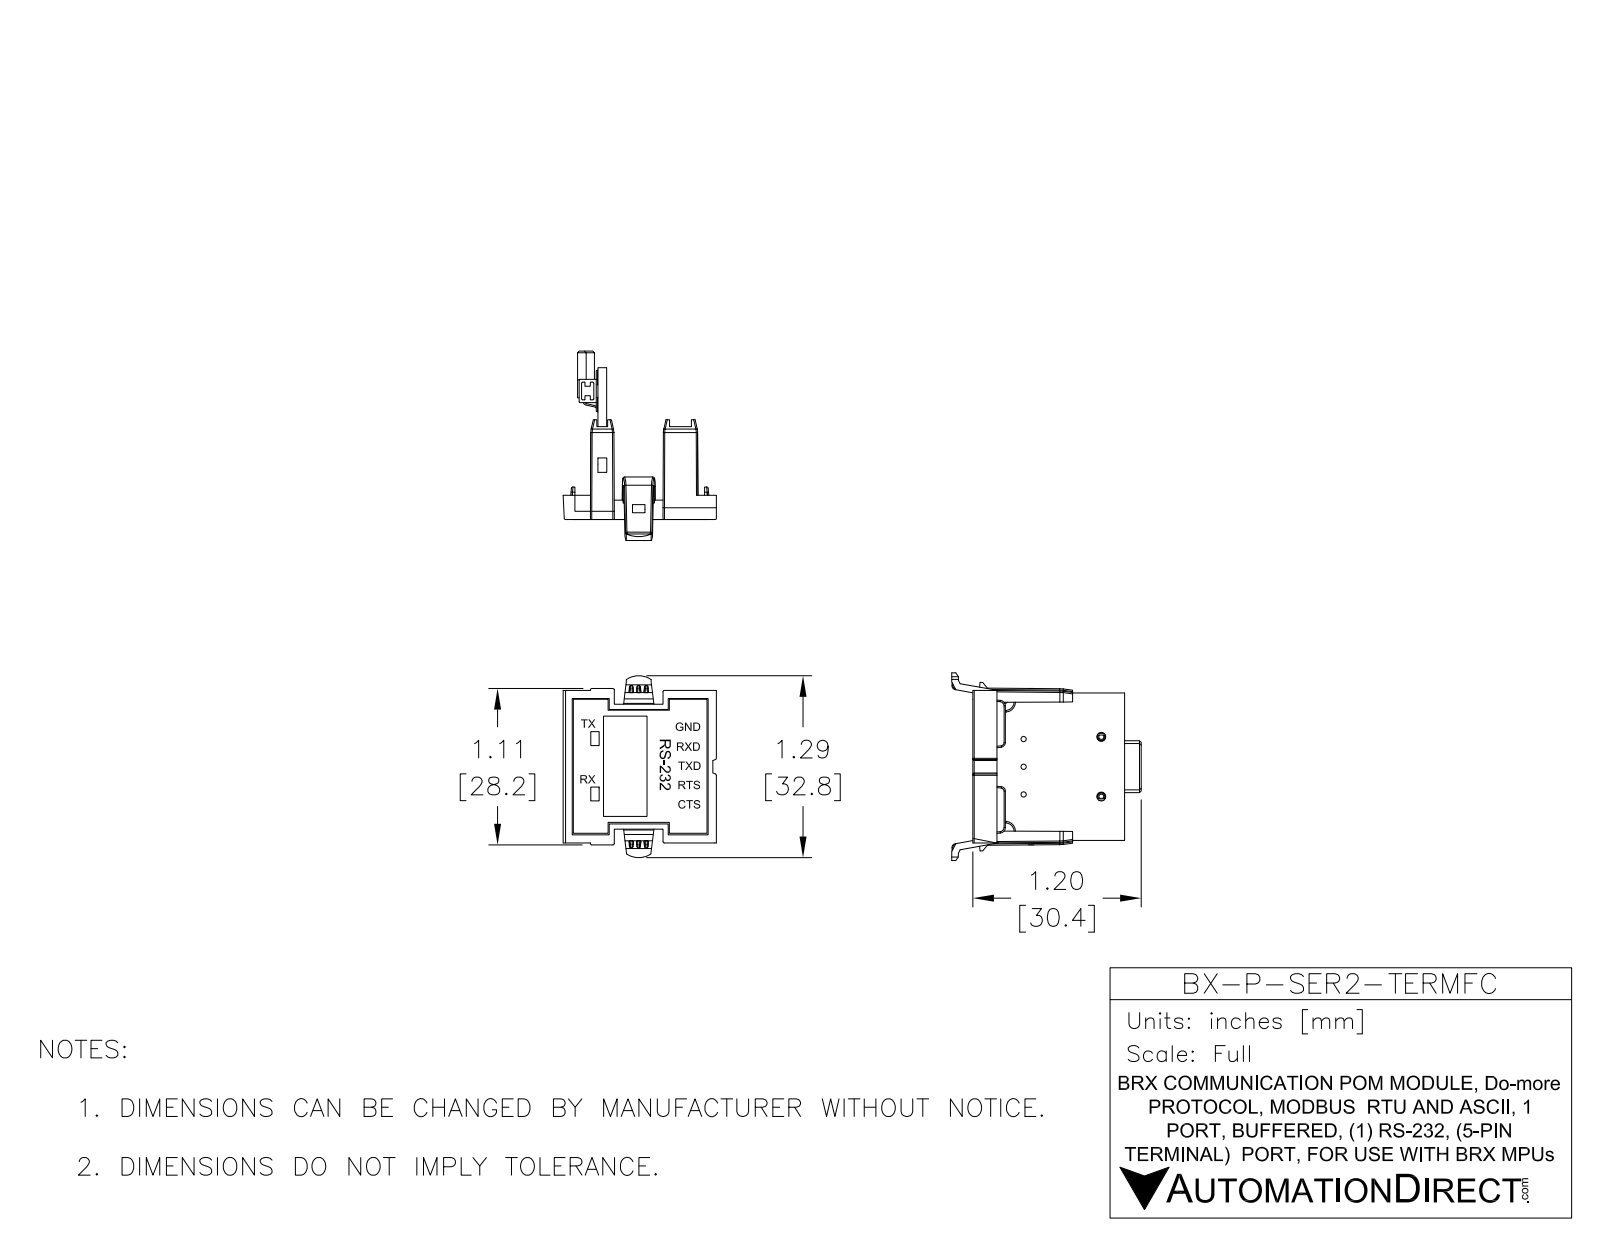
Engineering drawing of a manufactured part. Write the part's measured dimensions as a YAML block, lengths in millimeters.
part_name: "BX-P-SER2-TERMFC c r3"
step_written_by: "SolidWorks 2017 (AUTOMOTIVE_DESIGN)"
units: millimeters
bodies: {solids: 37, faces: 2056, planar: 1492, cylindrical: 367, other: 197}
overall_size: [41, 33.9, 27.5]
volume: 6190
surface_area: 10500
round_holes:
  - {diameter: 0.3, count: 5}
  - {diameter: 1, count: 5}
  - {diameter: 2, count: 5}
  - {diameter: 2.8, count: 5}
  - {diameter: 0.9, count: 3}
  - {diameter: 1.6, count: 2}
round_bosses_or_shafts:
  - {diameter: 2.6, count: 5}
  - {diameter: 0.3, count: 5}
partial_cylinders:
  - {radius: 0.1, count: 99}
  - {radius: 0.2, count: 27}
  - {radius: 0.3, count: 10}
  - {radius: 0.4, count: 10}
  - {radius: 0.3, count: 8}
  - {radius: 1.2, count: 5}
  - {radius: 1.8, count: 5}
  - {radius: 1.8, count: 5}
face_to_face_distances: [7, 1.6, 1.6, 3.5, 0.5, 1.7, 3, 8.4, 10.5, 0.7]
hole_center_spacings: [3.5, 7, 14.5, 10.5, 14, 14, 14, 15.7]
